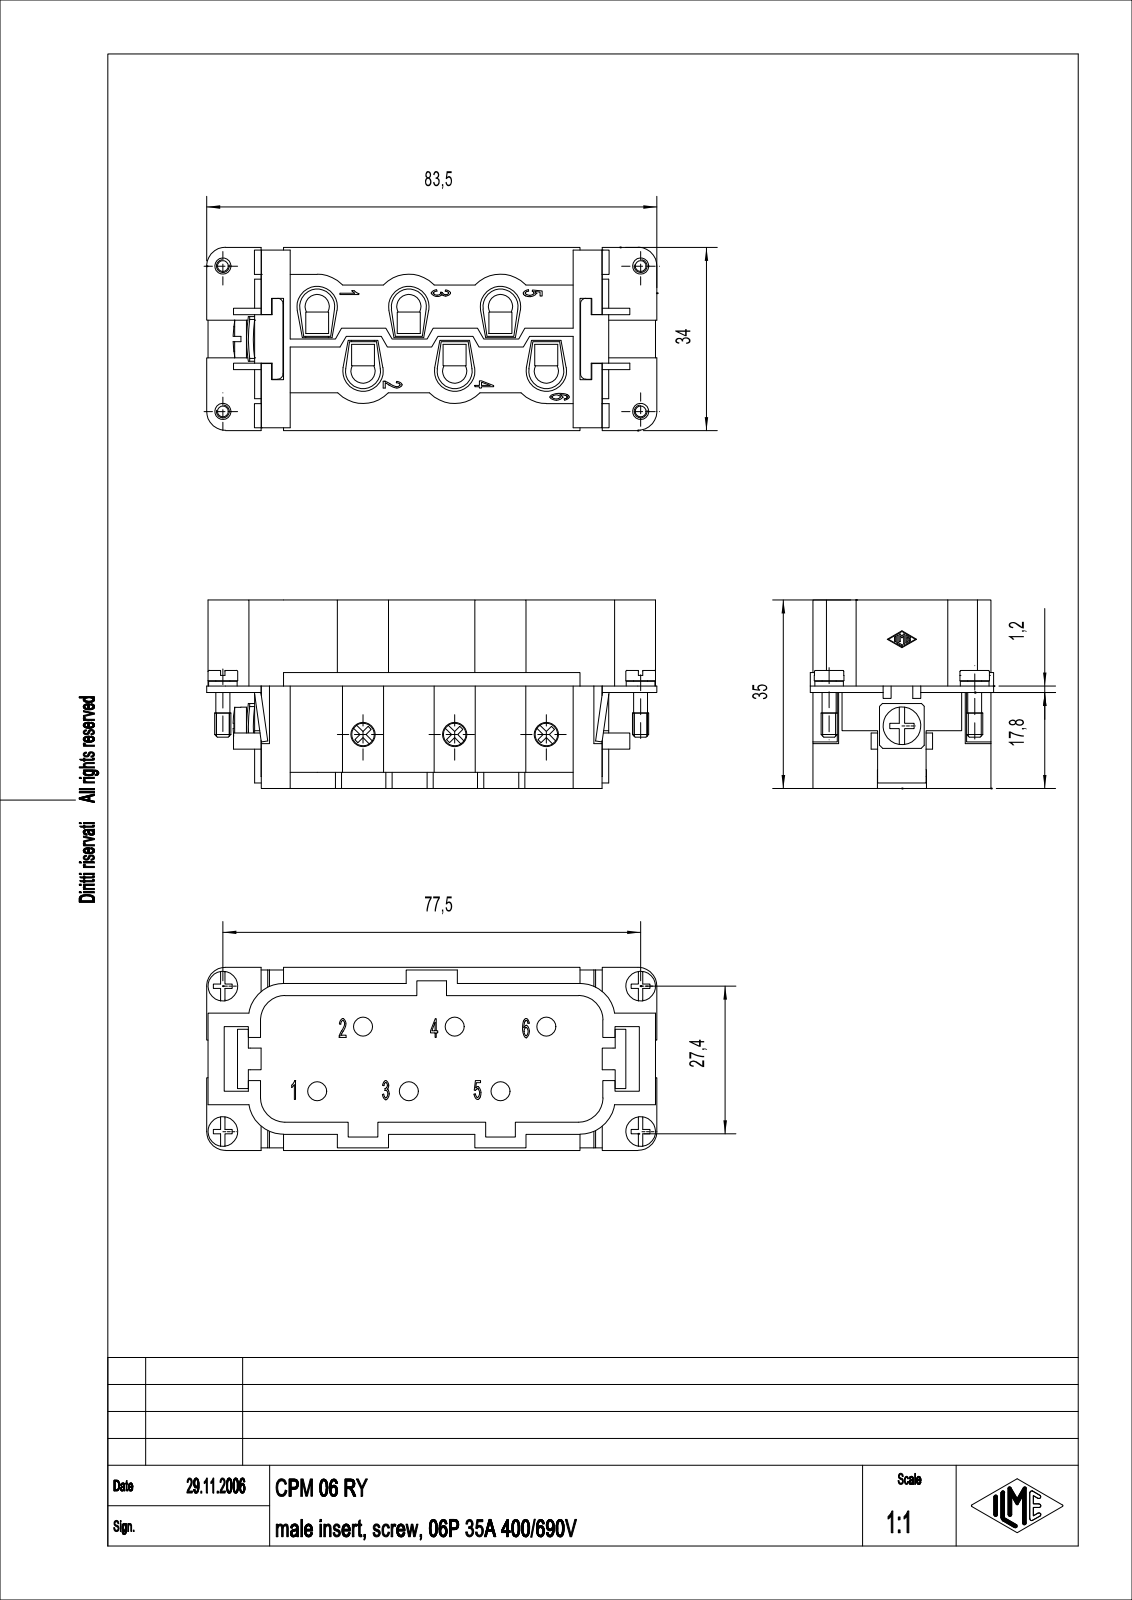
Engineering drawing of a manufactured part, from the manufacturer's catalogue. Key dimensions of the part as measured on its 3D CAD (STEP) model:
Part name (STEP PRODUCT): CPM 06 RY
STEP written by: Autodesk Inventor 7 (AUTOMOTIVE_DESIGN)
Units: millimetres
Bodies: 3 solids, 950 faces (538 planar, 140 cylindrical, 272 other)
Overall size (bounding box): 83.5 × 35 × 34
Volume: 37 800 mm³ · Surface area: 26 824 mm²
Round holes (diameter × count): ⌀4.5 ×12, ⌀3.24 ×1
Round bosses / shafts (diameter × count): ⌀4.2 ×6, ⌀3.5 ×6, ⌀5.5 ×2, ⌀5.3 ×2, ⌀3 ×2, ⌀2.6 ×2, ⌀7 ×1
Partial cylindrical surfaces — rounded edges, fillets, slot ends (radius × count): R0.1 ×14, R6.5 ×10, R3.25 ×6, R3.75 ×6, R4.5 ×4, R1 ×2, R2 ×2, R3.5 ×2
Main face-to-face distances: 2.5, 16, 18.5, 6.5, 2.25, 8, 4, 25.75, 3, 5.5
Hole centre spacings: 17, 8.5, 14.71, 34, 25.5, 28.18, 42.5, 44.16
